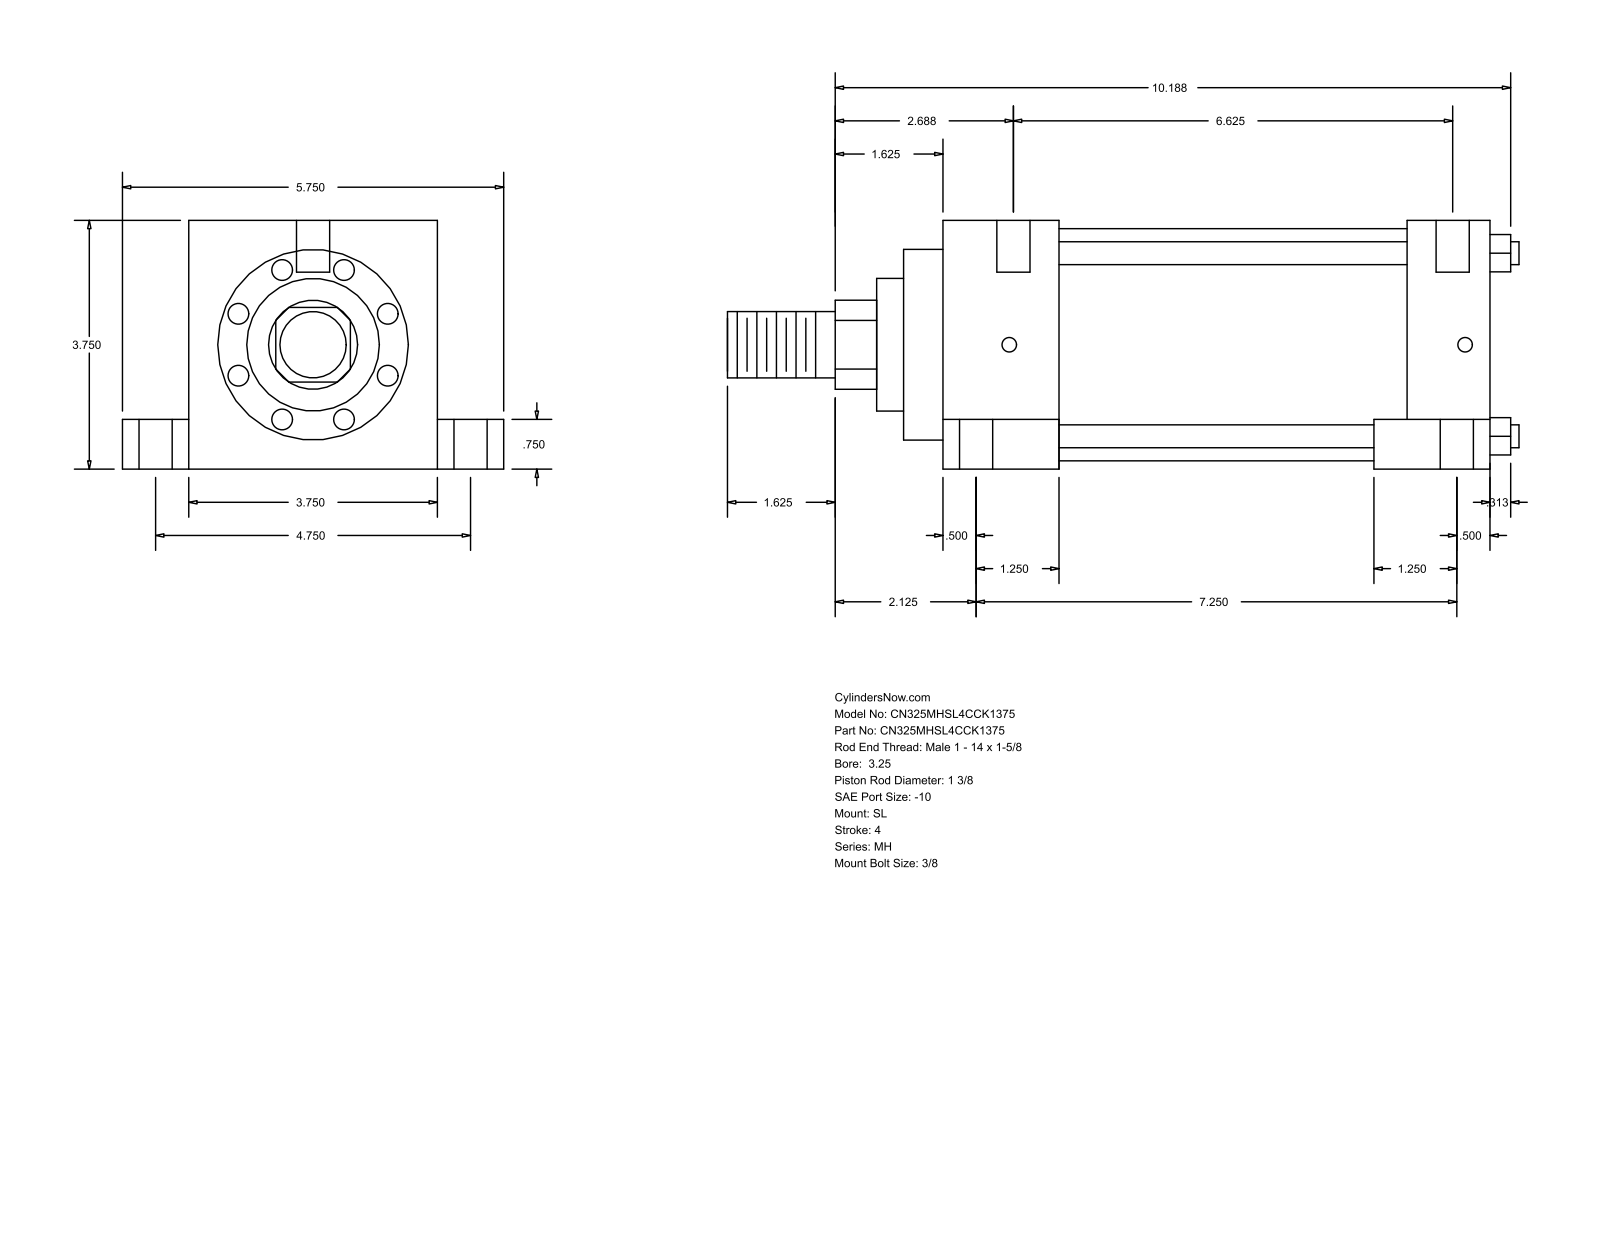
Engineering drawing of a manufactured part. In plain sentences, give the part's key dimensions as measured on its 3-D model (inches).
The part is named "MH_SL__0325_1.375". Its 3-D file was written by "GSSL Pune (CONFIG_CONTROL_DESIGN)". It is 0 solids with 110 faces: 77 planar, 33 cylindrical and 0 other. Overall it measures 11.937 by 5.75 by 3.75 inches. Round holes: 6 of diameter 0.5, 4 of diameter 0.219, 4 of diameter 0.75. Round bosses or shafts: 4 of diameter 0.345, 1 of diameter 3.5, 1 of diameter 2.875, 1 of diameter 2, 1 of diameter 1.375, 1 of diameter 1. Partial cylindrical surfaces (rounded edges, fillets, slot ends): 1 of radius 0.672. The main face-to-face distances are 3.75, 8.25, 1.75, 6.5, 1, 4.75, 0.75, 3, 7, 5.25. The hole center spacings are 2.376, 2.378, 2.427, 2.441, 4.75, 6.875, 7.097, 7.156.
